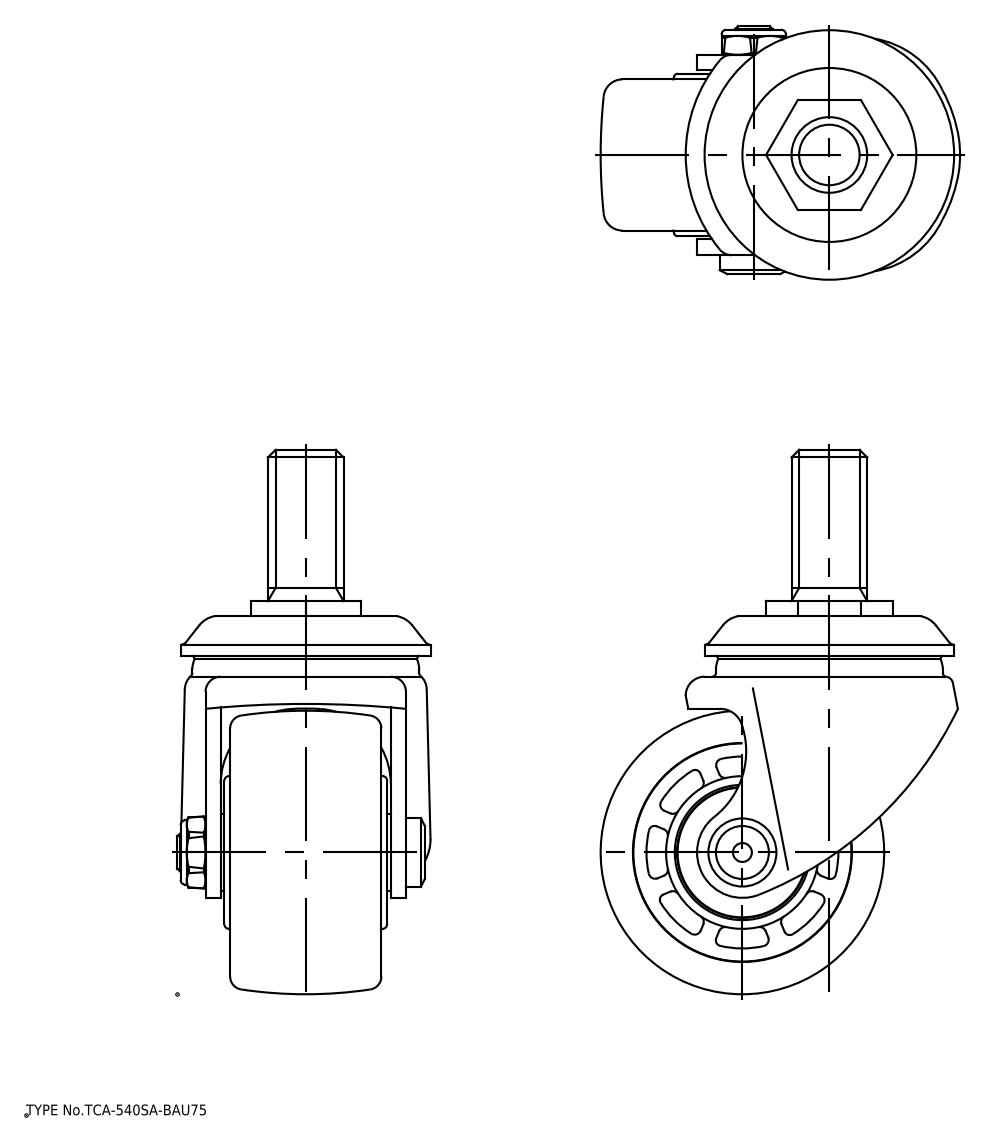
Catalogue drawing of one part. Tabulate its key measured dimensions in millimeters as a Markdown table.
| quantity | value |
| --- | --- |
| part name | wheel |
| STEP written by | spGate 19.8.4 (****-****-****-****) (AUTOMOTIVE_DESIGN) |
| units | millimeters |
| bodies | 2 solids, 209 faces (58 planar, 89 cylindrical, 62 other) |
| overall size | 144 × 94.47 × 69.5 |
| volume | 257 450 mm³ |
| surface area | 57 334 mm² |
| round holes (diameter × count) | 34.62 × 1, 54 × 1, 57.92 × 1 |
| round bosses / shafts (diameter × count) | 66 × 1, 60 × 1, 57.69 × 1, 40.38 × 1, 20.31 × 1, 20 × 1, 18 × 1, 17 × 1 |
| partial cylindrical surfaces (radius × count) | 1.73 × 24, 1.5 × 8, 5 × 3, 1 × 1, 2 × 1, 6 × 1, 12 × 1, 22 × 1 |
| main face-to-face distances | 42.5, 4, 2.5, 40, 20, 6.5, 1, 1.5, 46.5, 49 |
